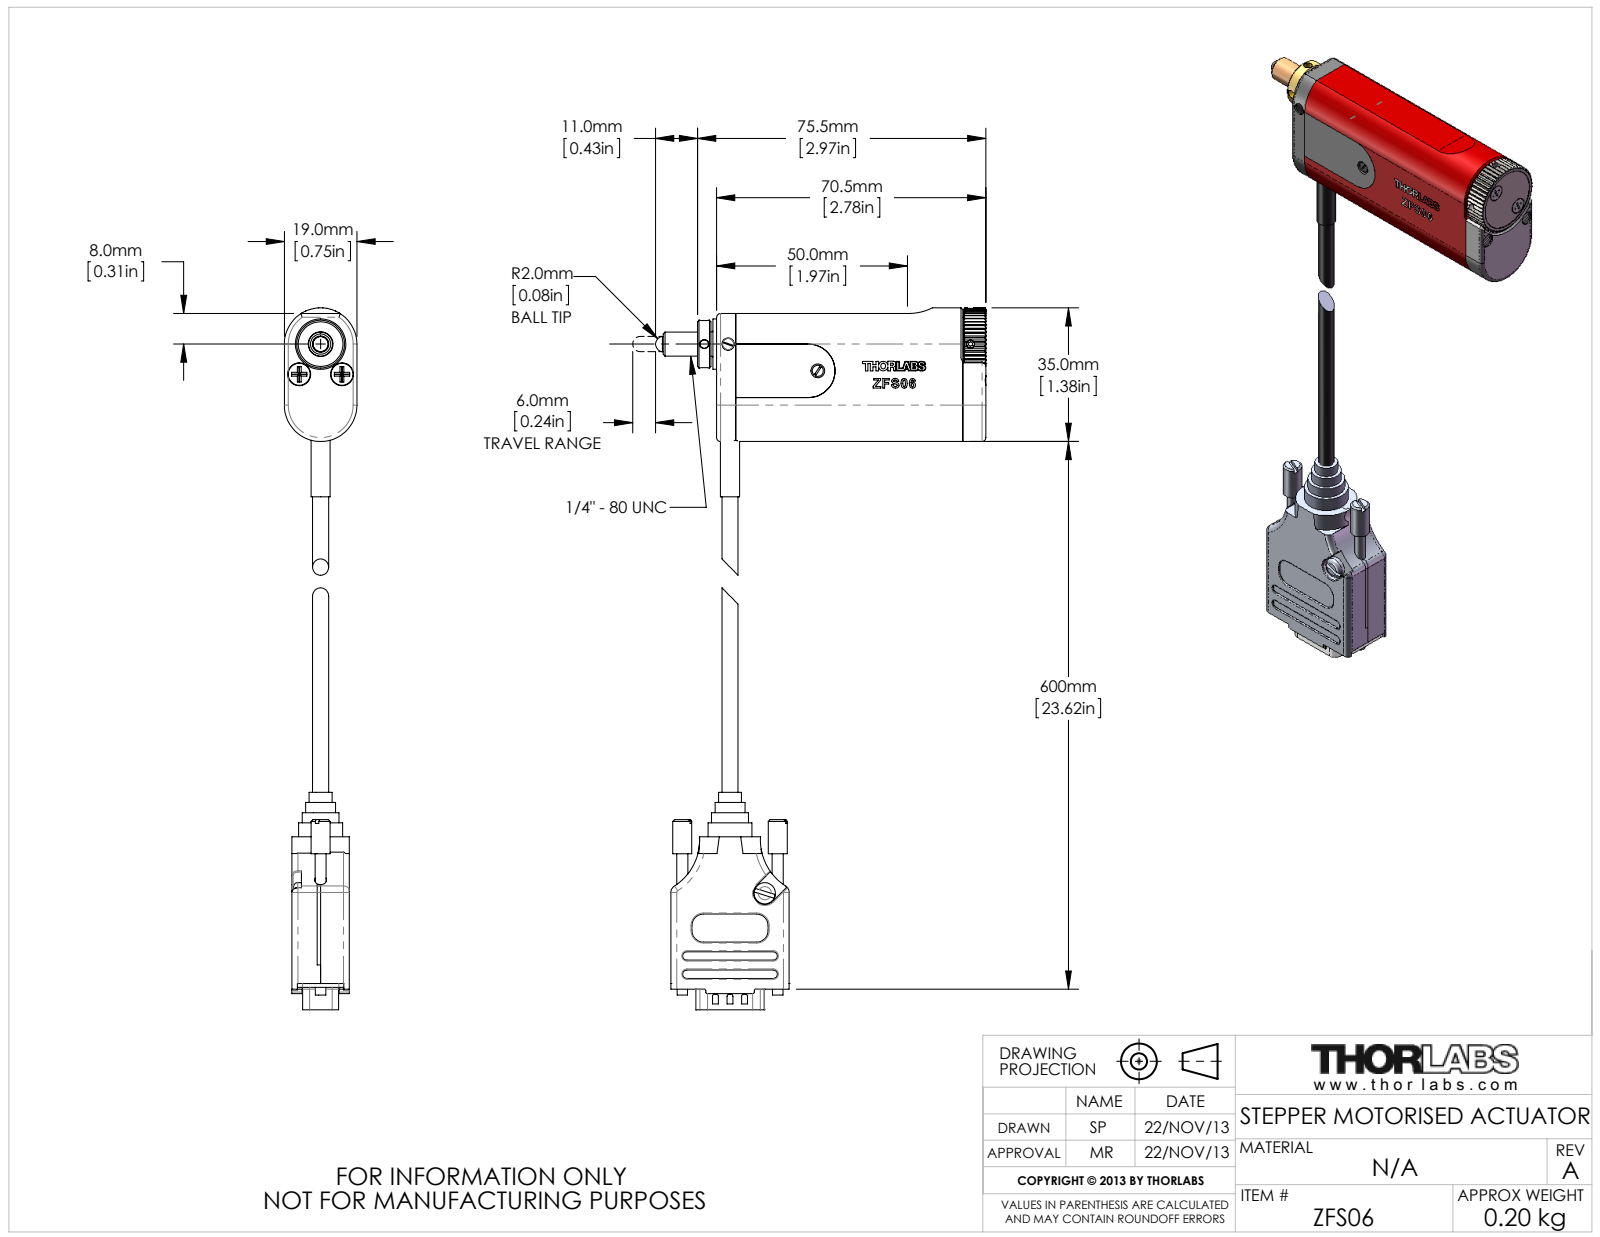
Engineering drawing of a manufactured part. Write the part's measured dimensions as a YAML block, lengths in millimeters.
part_name: "ZFS06"
step_written_by: "SolidWorks 2012 (AUTOMOTIVE_DESIGN)"
units: millimeters
bodies: {solids: 0, faces: 870, planar: 390, cylindrical: 269, other: 211}
overall_size: [183.78, 86.5, 19]
round_holes:
  - {diameter: 2.1, count: 2}
  - {diameter: 2.2, count: 2}
  - {diameter: 3.05, count: 2}
  - {diameter: 3.6, count: 2}
  - {diameter: 6, count: 2}
  - {diameter: 2.5, count: 1}
  - {diameter: 3.2, count: 1}
  - {diameter: 4.3, count: 1}
  - {diameter: 16.5, count: 1}
round_bosses_or_shafts:
  - {diameter: 0.99, count: 15}
  - {diameter: 5.56, count: 2}
  - {diameter: 4.97, count: 2}
  - {diameter: 4.08, count: 2}
  - {diameter: 2.89, count: 2}
  - {diameter: 2.73, count: 2}
  - {diameter: 16.3, count: 1}
  - {diameter: 13.2, count: 1}
partial_cylinders:
  - {radius: 0.25, count: 23}
  - {radius: 1.52, count: 12}
  - {radius: 0.51, count: 7}
  - {radius: 1, count: 5}
  - {radius: 0.38, count: 4}
  - {radius: 2.03, count: 4}
  - {radius: 3.05, count: 4}
  - {radius: 1.1, count: 3}
face_to_face_distances: [19, 3.4, 15.6, 2.01, 16.99, 1.39, 13.59, 12.2, 14.98, 0.35]
hole_center_spacings: [2.26, 9.68, 11.92, 12.9, 69.75, 5.75, 6.25, 11.2]
